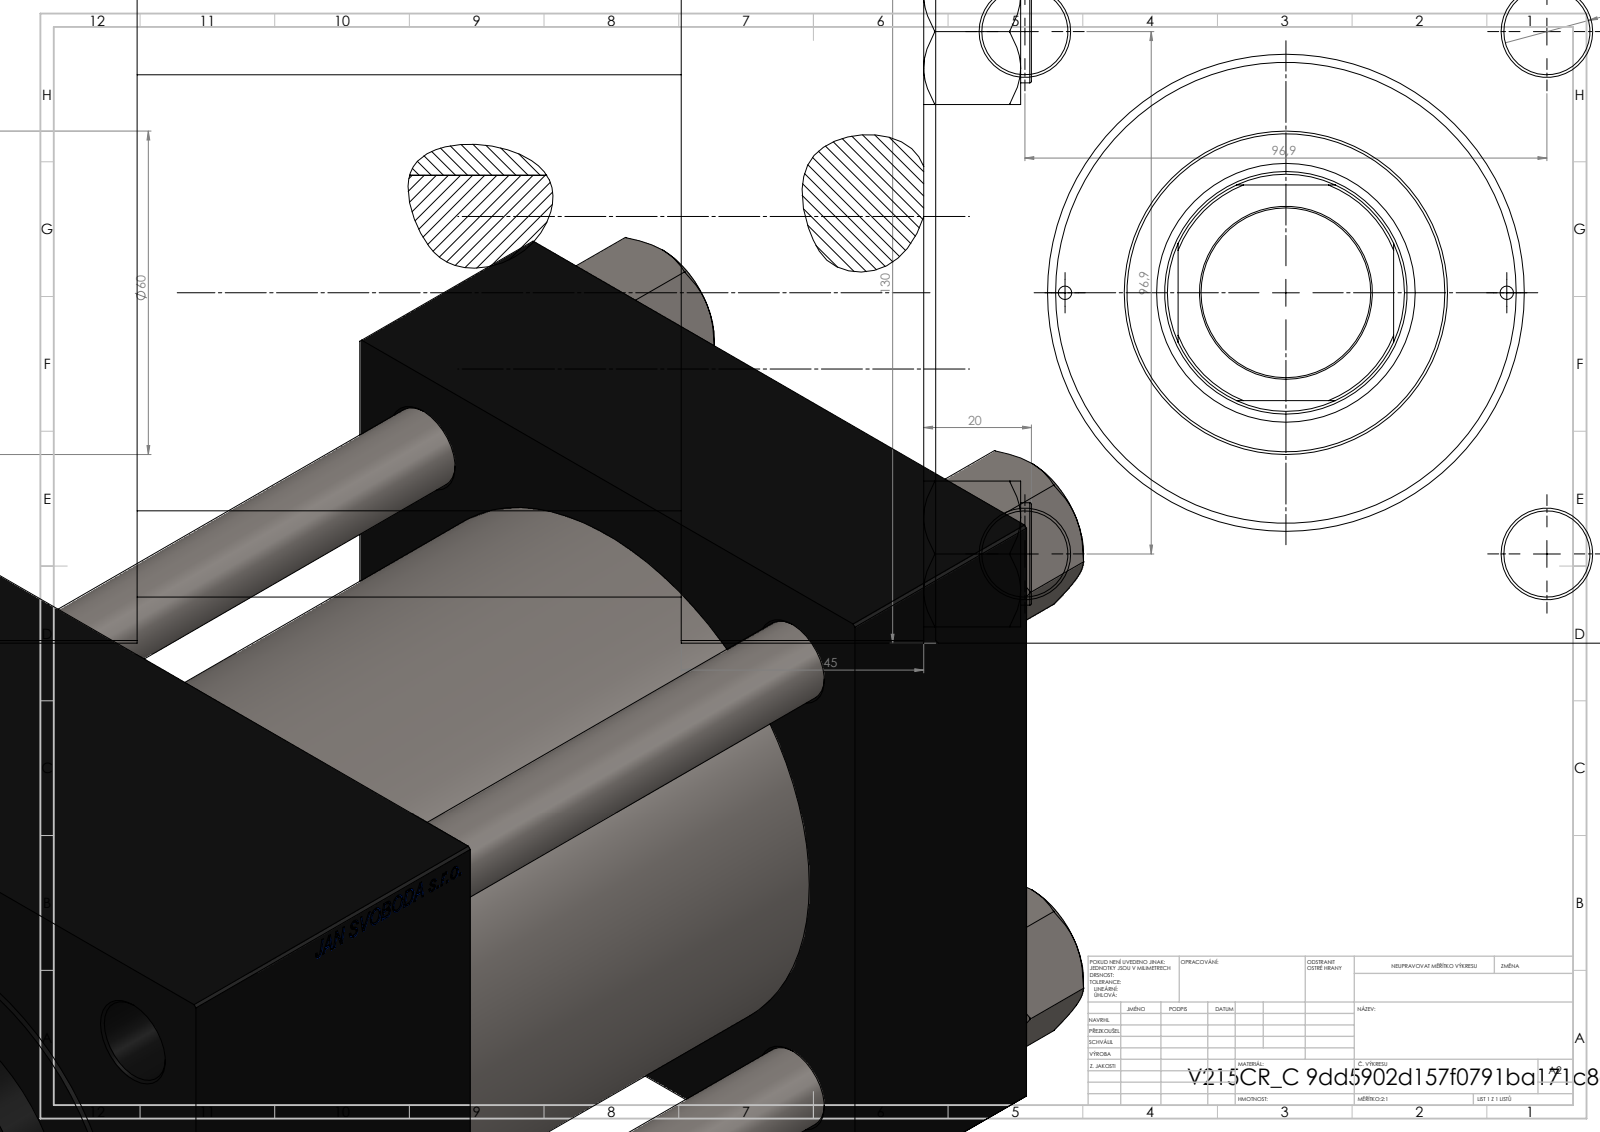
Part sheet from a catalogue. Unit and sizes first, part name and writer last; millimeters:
Units: millimetres
Overall size (bounding box): 273 × 130 × 130
Round holes (diameter × count): ⌀16 ×4, ⌀2.5 ×2, ⌀7 ×2, ⌀26.44 ×2, ⌀35 ×2, ⌀31.5 ×1, ⌀45 ×1, ⌀48 ×1, ⌀76 ×1, ⌀85.5 ×1, ⌀100 ×1
Round bosses / shafts (diameter × count): ⌀19 ×4, ⌀106 ×1, ⌀60 ×1
Partial cylindrical surfaces — rounded edges, fillets, slot ends (radius × count): R22 ×1
Main face-to-face distances: 130, 45, 218, 173, 146, 101, 72, 96, 51, 50
Hole centre spacings: 49.02, 68.52, 96.9, 101.73, 41, 137.04, 82, 148.5
Volume: 2 526 000 mm³ · Surface area: 356 154 mm²
Bodies: 11 solids, 1202 faces (576 planar, 90 cylindrical, 536 other)
Part name (STEP PRODUCT): V215_VC_A; NUT_M5_C; V215CR_C_TYCINKA; V215CR_VCP_C (+1 more)
STEP written by: SolidWorks 2019 (CONFIG_CONTROL_DESIGN)
